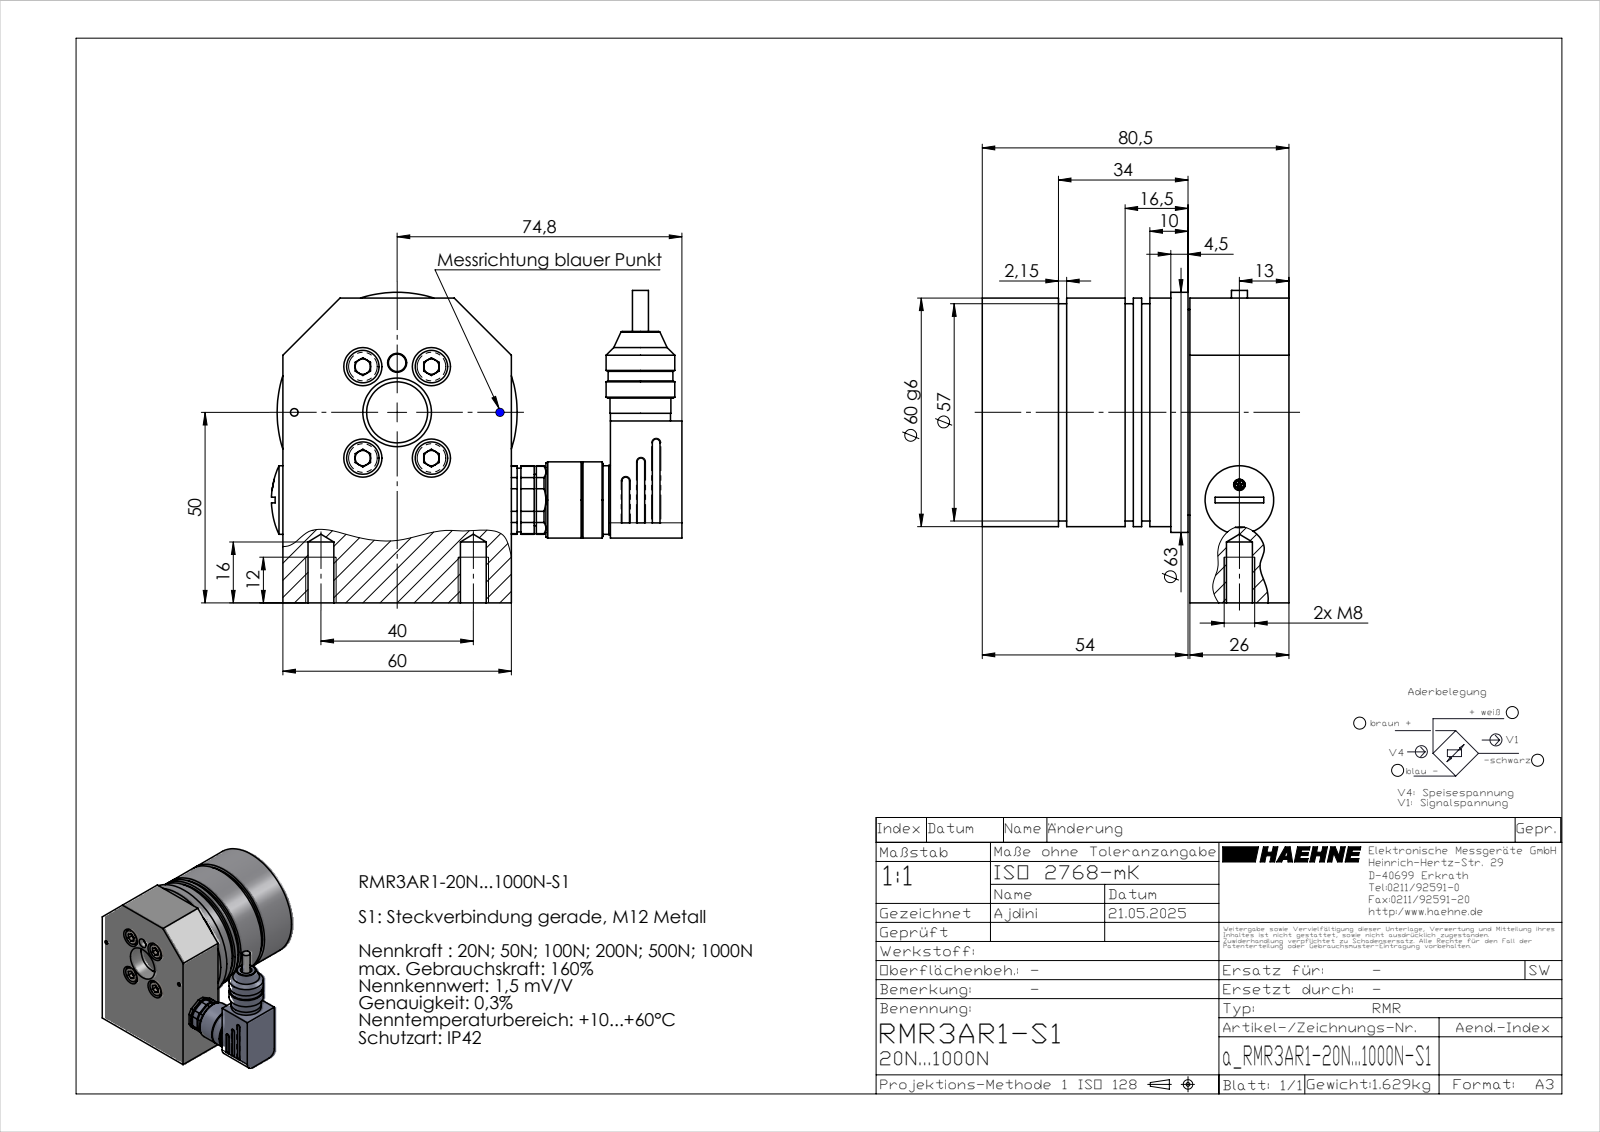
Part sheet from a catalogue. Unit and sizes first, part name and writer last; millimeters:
Units: millimetres
Overall size (bounding box): 107.74 × 81.98 × 80.5
Round holes (diameter × count): ⌀4.2 ×4, ⌀5.3 ×4, ⌀10 ×4, ⌀2 ×2, ⌀6.8 ×2, ⌀0.64 ×1, ⌀3 ×1, ⌀4.5 ×1, ⌀5 ×1, ⌀6 ×1, ⌀8.37 ×1, ⌀11.5 ×1
Round bosses / shafts (diameter × count): ⌀0.86 ×5, ⌀8.5 ×4, ⌀5 ×4, ⌀1.5 ×4, ⌀1 ×4, ⌀18 ×2, ⌀16 ×2, ⌀63 ×1
Partial cylindrical surfaces — rounded edges, fillets, slot ends (radius × count): R0.2 ×12, R1 ×11, R0.3 ×6, R4 ×2, R0.57 ×1, R0.65 ×1, R0.77 ×1, R3.5 ×1
Main face-to-face distances: 11.5, 48.5, 37, 26, 73, 54.5, 15, 11, 62, 47
Hole centre spacings: 15, 21.63, 37.95, 9.06, 18, 24, 26.57, 27
Volume: 250 609 mm³ · Surface area: 77 185 mm²
Bodies: 17 solids, 556 faces (279 planar, 181 cylindrical, 96 other)
Part name (STEP PRODUCT): a_RMR3AR1-20N...1000N-S1
STEP written by: SolidWorks 2023 (AUTOMOTIVE_DESIGN)
